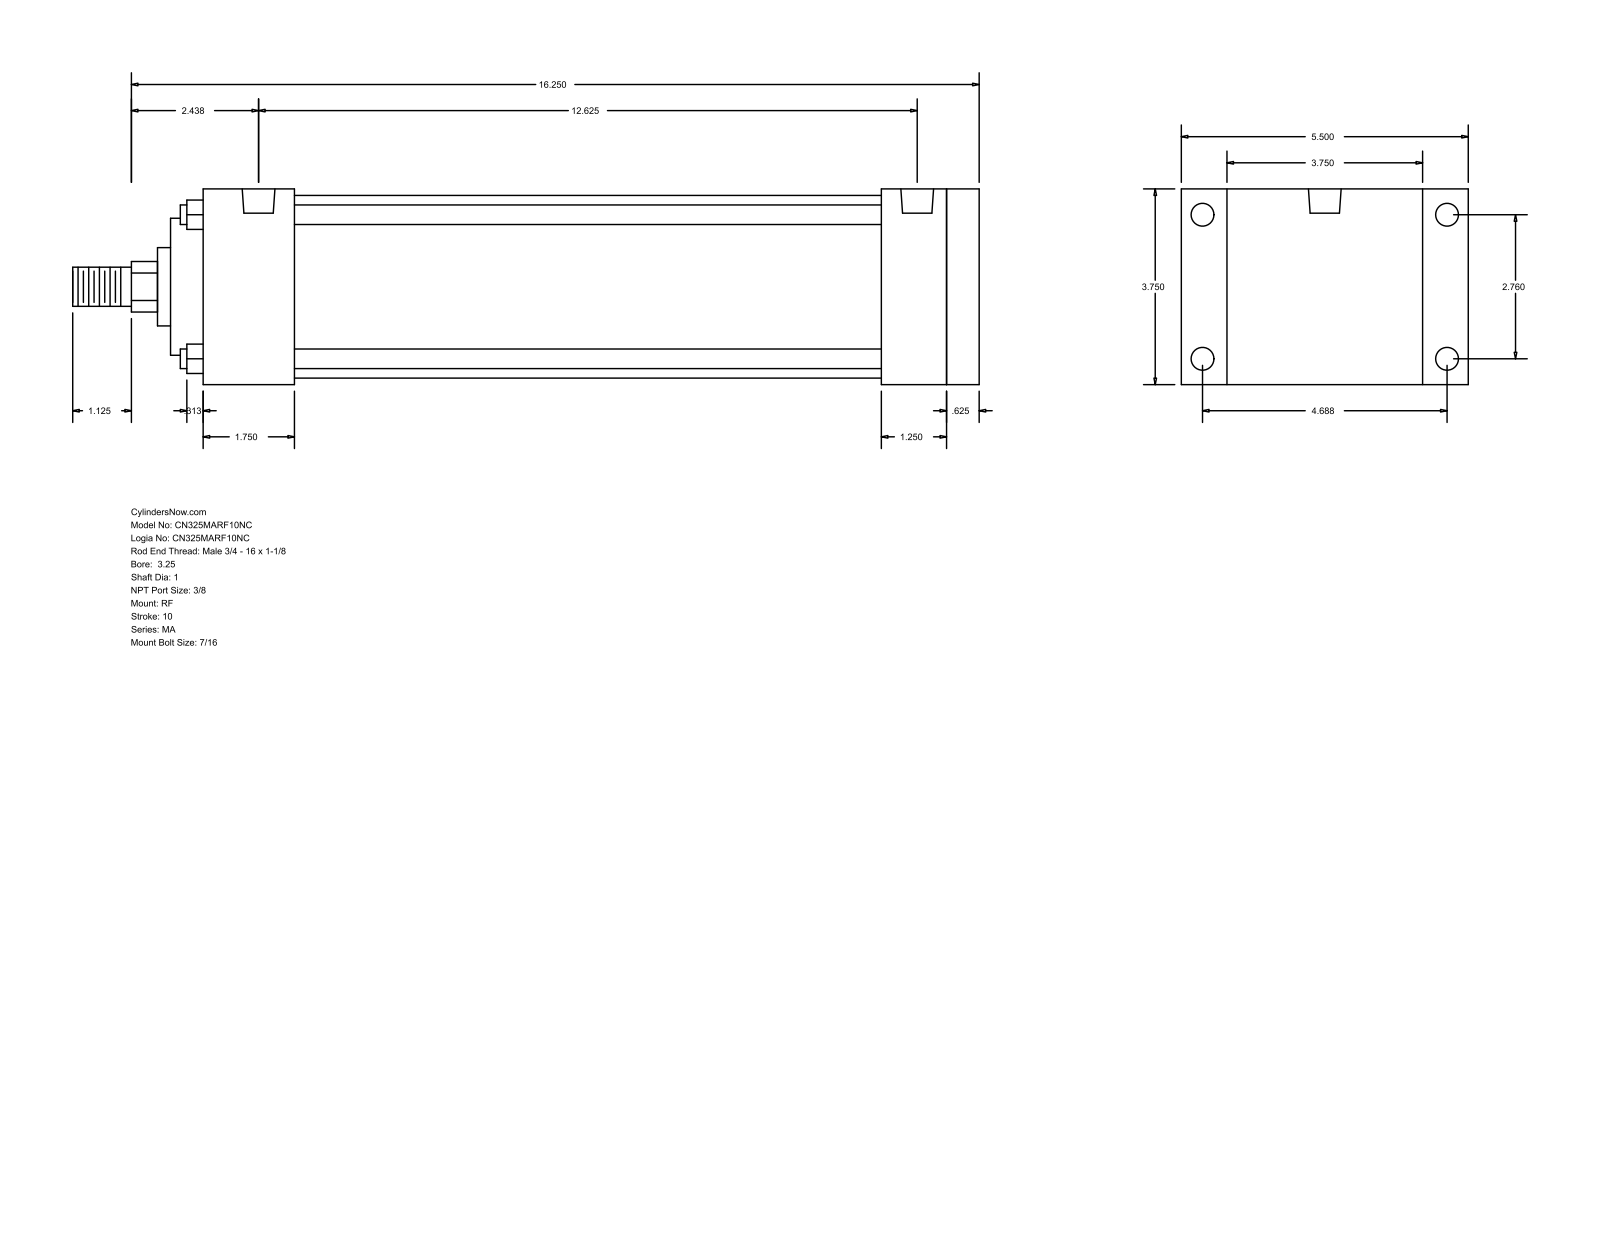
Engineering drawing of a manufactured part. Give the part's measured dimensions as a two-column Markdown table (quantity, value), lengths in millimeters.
| quantity | value |
| --- | --- |
| part name | MA_RF__0325_1 |
| STEP written by | GSSL Pune (CONFIG_CONTROL_DESIGN) |
| units | millimeters |
| bodies | 0 solids, 94 faces (65 planar, 29 cylindrical, 0 other) |
| overall size | 441.32 × 139.7 × 95.25 |
| round holes (diameter × count) | 11.11 × 8, 15.93 × 2 |
| round bosses / shafts (diameter × count) | 9.53 × 4, 88.9 × 1, 66.67 × 1, 38.1 × 1, 25.4 × 1, 19.05 × 1 |
| partial cylindrical surfaces (radius × count) | 12.29 × 1 |
| main face-to-face distances | 95.24, 377.83, 15.87, 361.96, 22.23, 117.47, 330.2, 31.76, 47.63, 44.46 |
| hole center spacings | 70.1, 119.06, 138.16, 311.15, 4.76, 4.77, 315.91, 315.92 |
